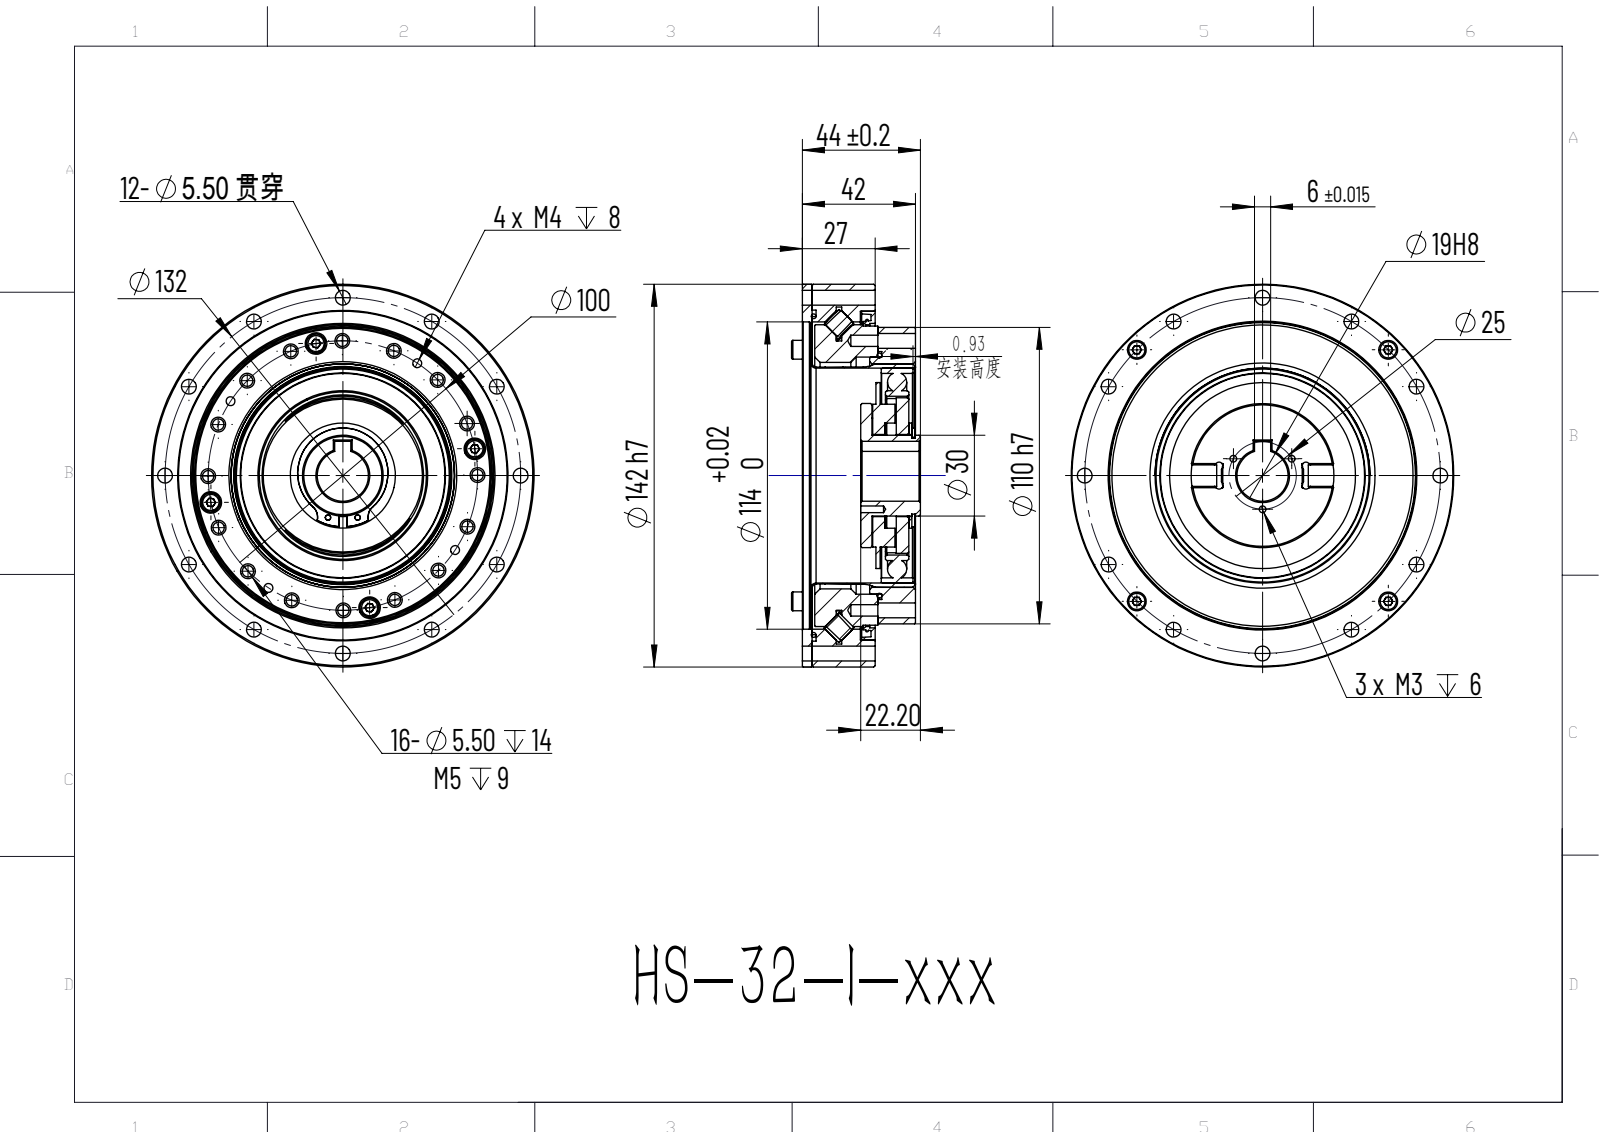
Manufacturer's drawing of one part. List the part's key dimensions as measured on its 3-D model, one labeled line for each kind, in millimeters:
Part name (STEP PRODUCT): HS-32-I; hexagon socket head cap screws gb_GB_FASTENER_SCREWS_HSHCS M4X12-C; ????-STXB-32080-01; O????-?90X?1.8_?? (+8 more)
STEP written by: ONSHAPE BY PTC INC, 1.201 (AP242_MANAGED_MODEL_BASED_3D_ENGINEERING_MIM_LF)
Units: millimetres
Bodies: 94 solids, 1096 faces (637 planar, 267 cylindrical, 192 other)
Overall size (bounding box): 142 × 142 × 47.8
Volume: 351 764 mm³ · Surface area: 200 266 mm²
Round holes (diameter × count): ⌀5.5 ×28, ⌀4.2 ×16, ⌀3.3 ×12, ⌀4.5 ×8, ⌀2.5 ×4, ⌀8 ×4, ⌀2 ×2, ⌀3.4 ×1, ⌀6 ×1, ⌀19 ×1, ⌀27.9 ×1, ⌀30.5 ×1
Round bosses / shafts (diameter × count): ⌀8 ×36, ⌀7 ×8, ⌀4 ×8, ⌀142 ×1, ⌀118 ×1, ⌀112 ×1, ⌀111 ×1, ⌀110 ×1
Partial cylindrical surfaces — rounded edges, fillets, slot ends (radius × count): R4 ×36, R4.03 ×36, R5 ×2, R16.75 ×1, R19.93 ×1
Main face-to-face distances: 1, 23.4, 24.4, 3.6, 27, 28, 3.33, 23.67, 24.67, 1.5
Hole centre spacings: 66, 93.34, 19.51, 34.16, 65.99, 114.32, 127.5, 130.87
